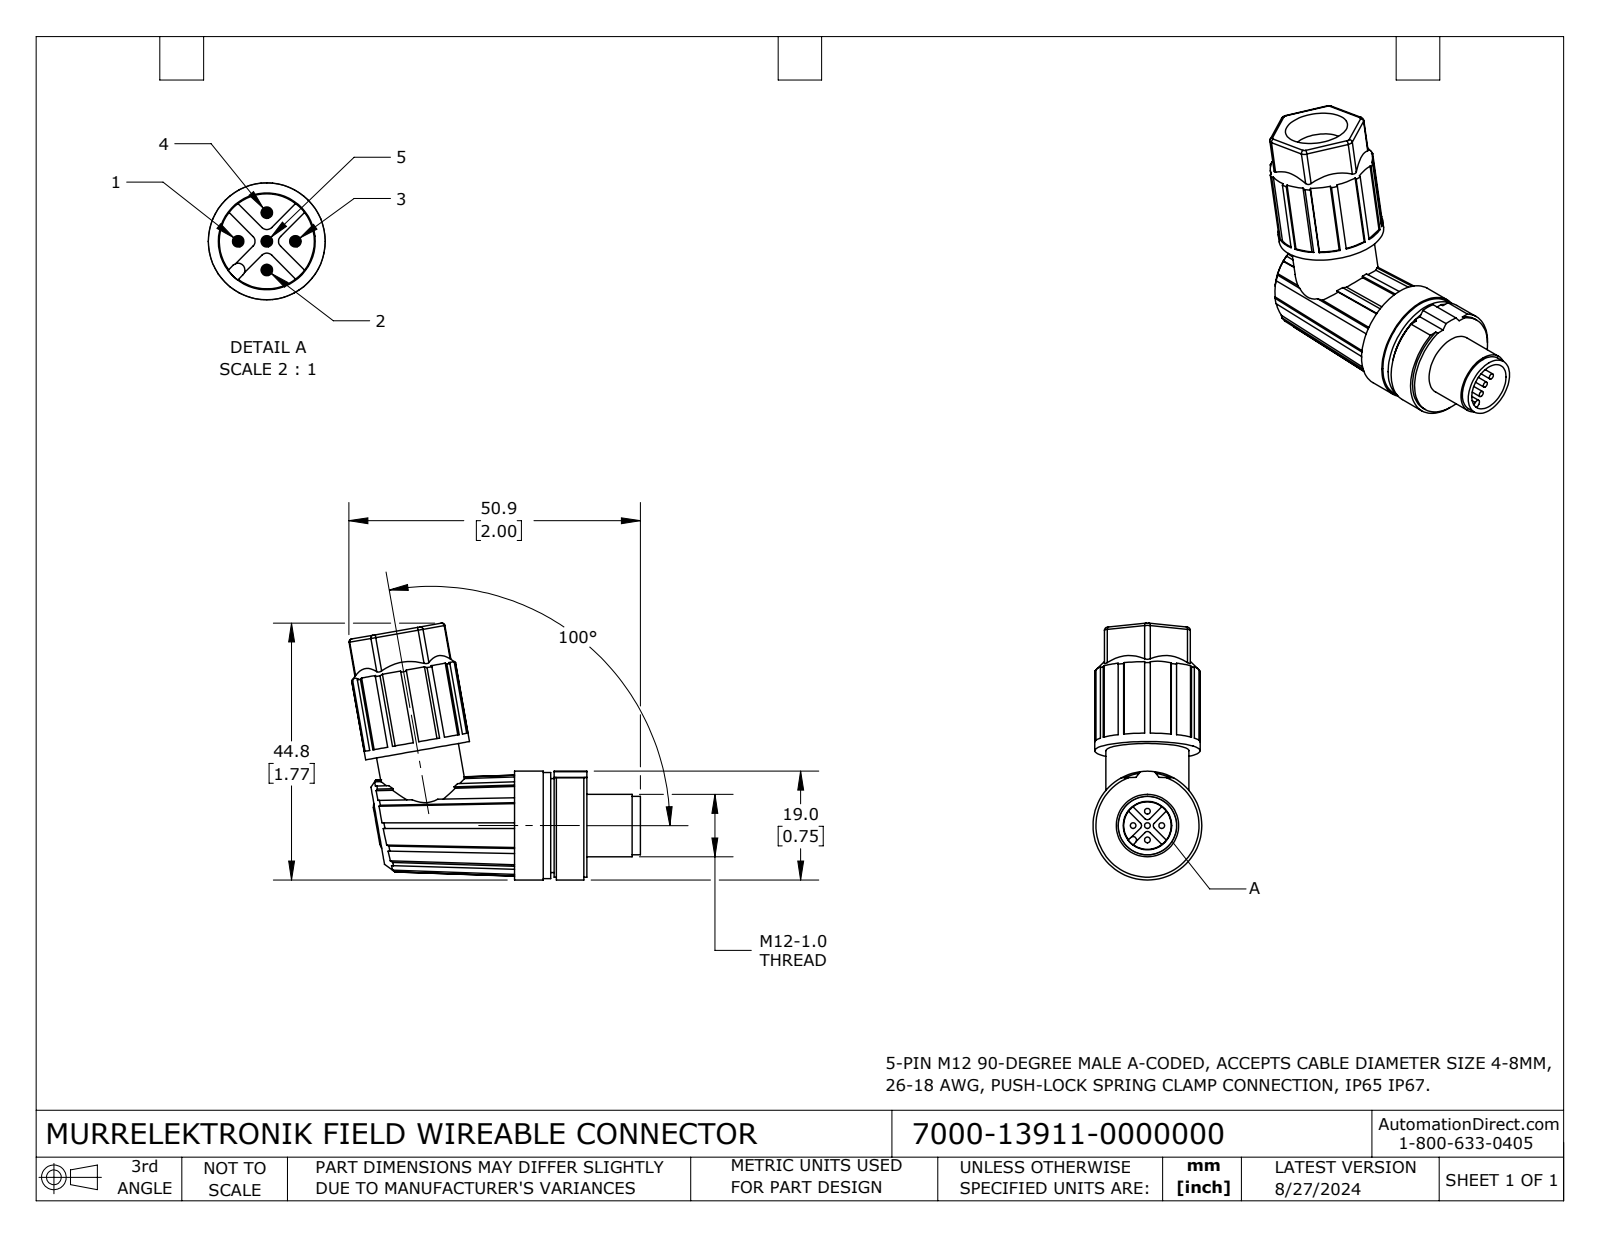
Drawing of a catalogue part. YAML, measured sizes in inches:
part_name: "7000-13911-0000000"
step_written_by: "SolidWorks 2023 (CONFIG_CONTROL_DESIGN)"
units: inches
bodies: {solids: 1, faces: 236, planar: 119, cylindrical: 68, other: 49}
overall_size: [2.003, 1.766, 0.748]
volume: 0.762
surface_area: 9.563
round_holes:
  - {diameter: 0.335, count: 1}
  - {diameter: 0.354, count: 1}
round_bosses_or_shafts:
  - {diameter: 0.039, count: 5}
  - {diameter: 0.748, count: 1}
  - {diameter: 0.728, count: 1}
  - {diameter: 0.724, count: 1}
  - {diameter: 0.709, count: 1}
  - {diameter: 0.646, count: 1}
  - {diameter: 0.571, count: 1}
  - {diameter: 0.429, count: 1}
partial_cylinders:
  - {radius: 0.02, count: 6}
  - {radius: 0.039, count: 6}
  - {radius: 0.024, count: 5}
  - {radius: 0.354, count: 1}
face_to_face_distances: [0.591, 0.248, 0.835, 0.039, 0.496, 0.697, 0.224, 0.024, 0.272, 0.276]
